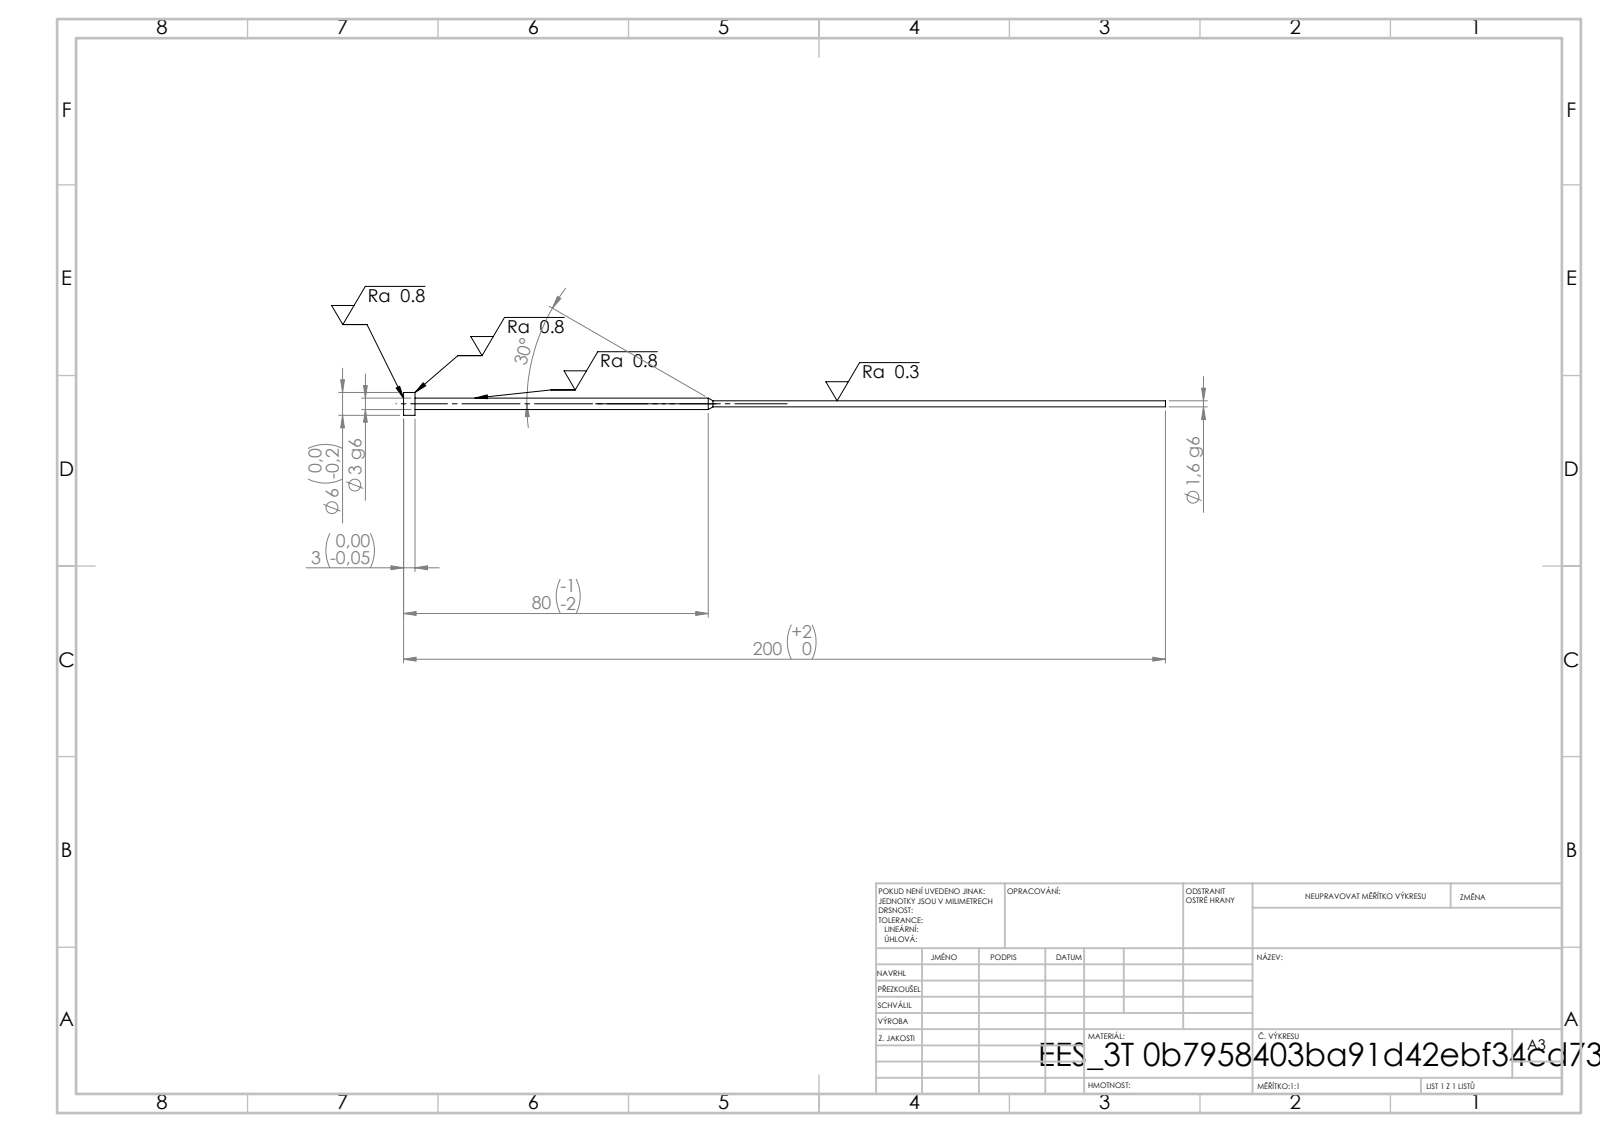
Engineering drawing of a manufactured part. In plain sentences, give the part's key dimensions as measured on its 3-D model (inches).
Its 3-D file was written by "SolidWorks 2019 (CONFIG_CONTROL_DESIGN)". It is 1 solid with 11 faces: 3 planar, 6 cylindrical and 2 other. Overall it measures 7.874 by 0.236 by 0.236 inches. Its volume is 0.053 cubic inches and its surface area 2.234 square inches. Round bosses or shafts: 1 of diameter 0.236, 1 of diameter 0.118, 1 of diameter 0.063. The main face-to-face distances are 0.118, 7.756, 7.874.
